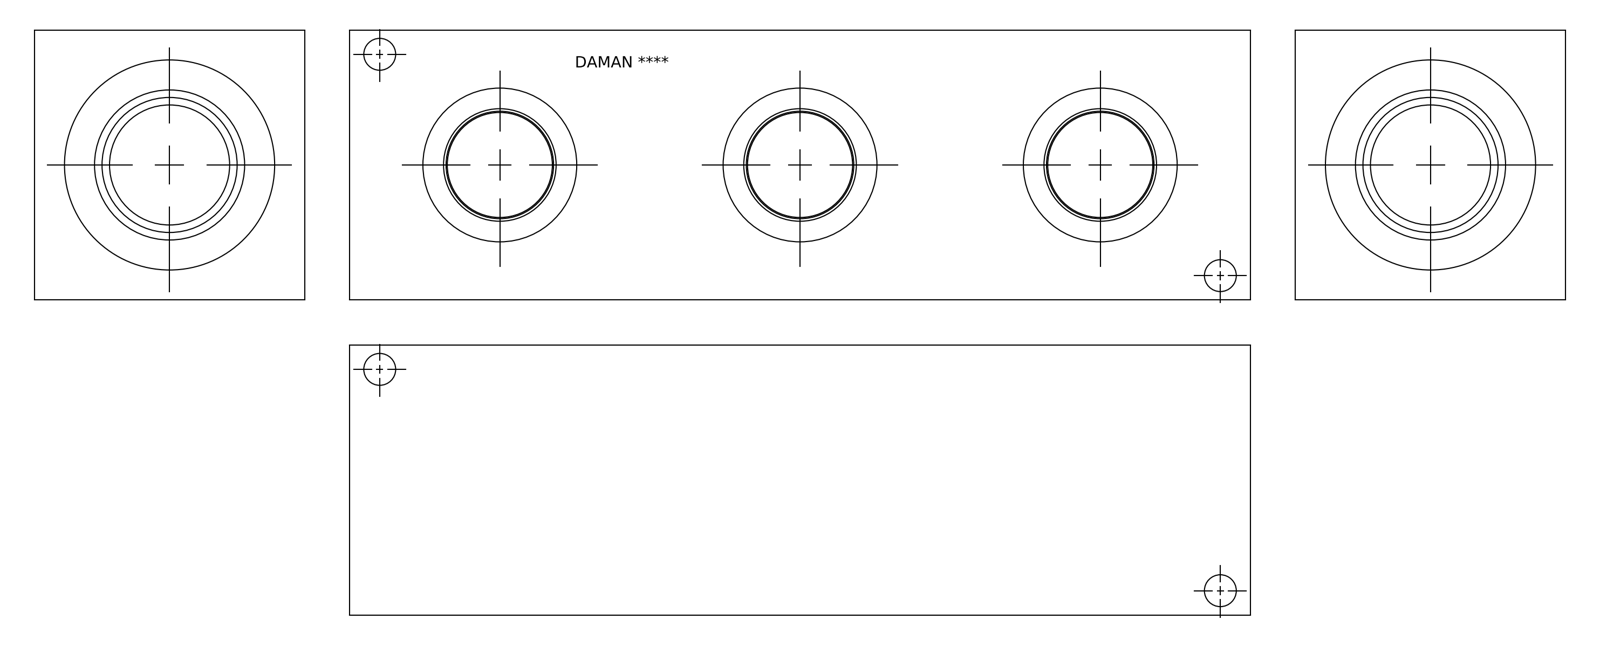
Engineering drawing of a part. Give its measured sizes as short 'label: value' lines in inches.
name: Part_+H0000324S_3D
written by: Autodesk Inventor 2020 (AUTOMOTIVE_DESIGN)
unit: in
bodies: 1 solid, 383 faces (228 planar, 33 cylindrical, 122 other)
size: 15 × 4.5 × 4.5
volume: 272.3 in³; area: 384.1 in²
holes: 4× ⌀0.531, 3× ⌀1.794, 3× ⌀1.875, 3× ⌀1.892, 3× ⌀2.564, 2× ⌀1.688, 1× ⌀1.75, 1× ⌀2, 1× ⌀2.419, 1× ⌀2.5, 1× ⌀2.518, 1× ⌀3.47
face distances: 4.5, 0.031, 15, 14.969, 4.469, 14.938, 0.781, 0.75, 3.719, 14.219
hole spacings: 2.72, 5, 7.239, 12.141, 14.478, 10
